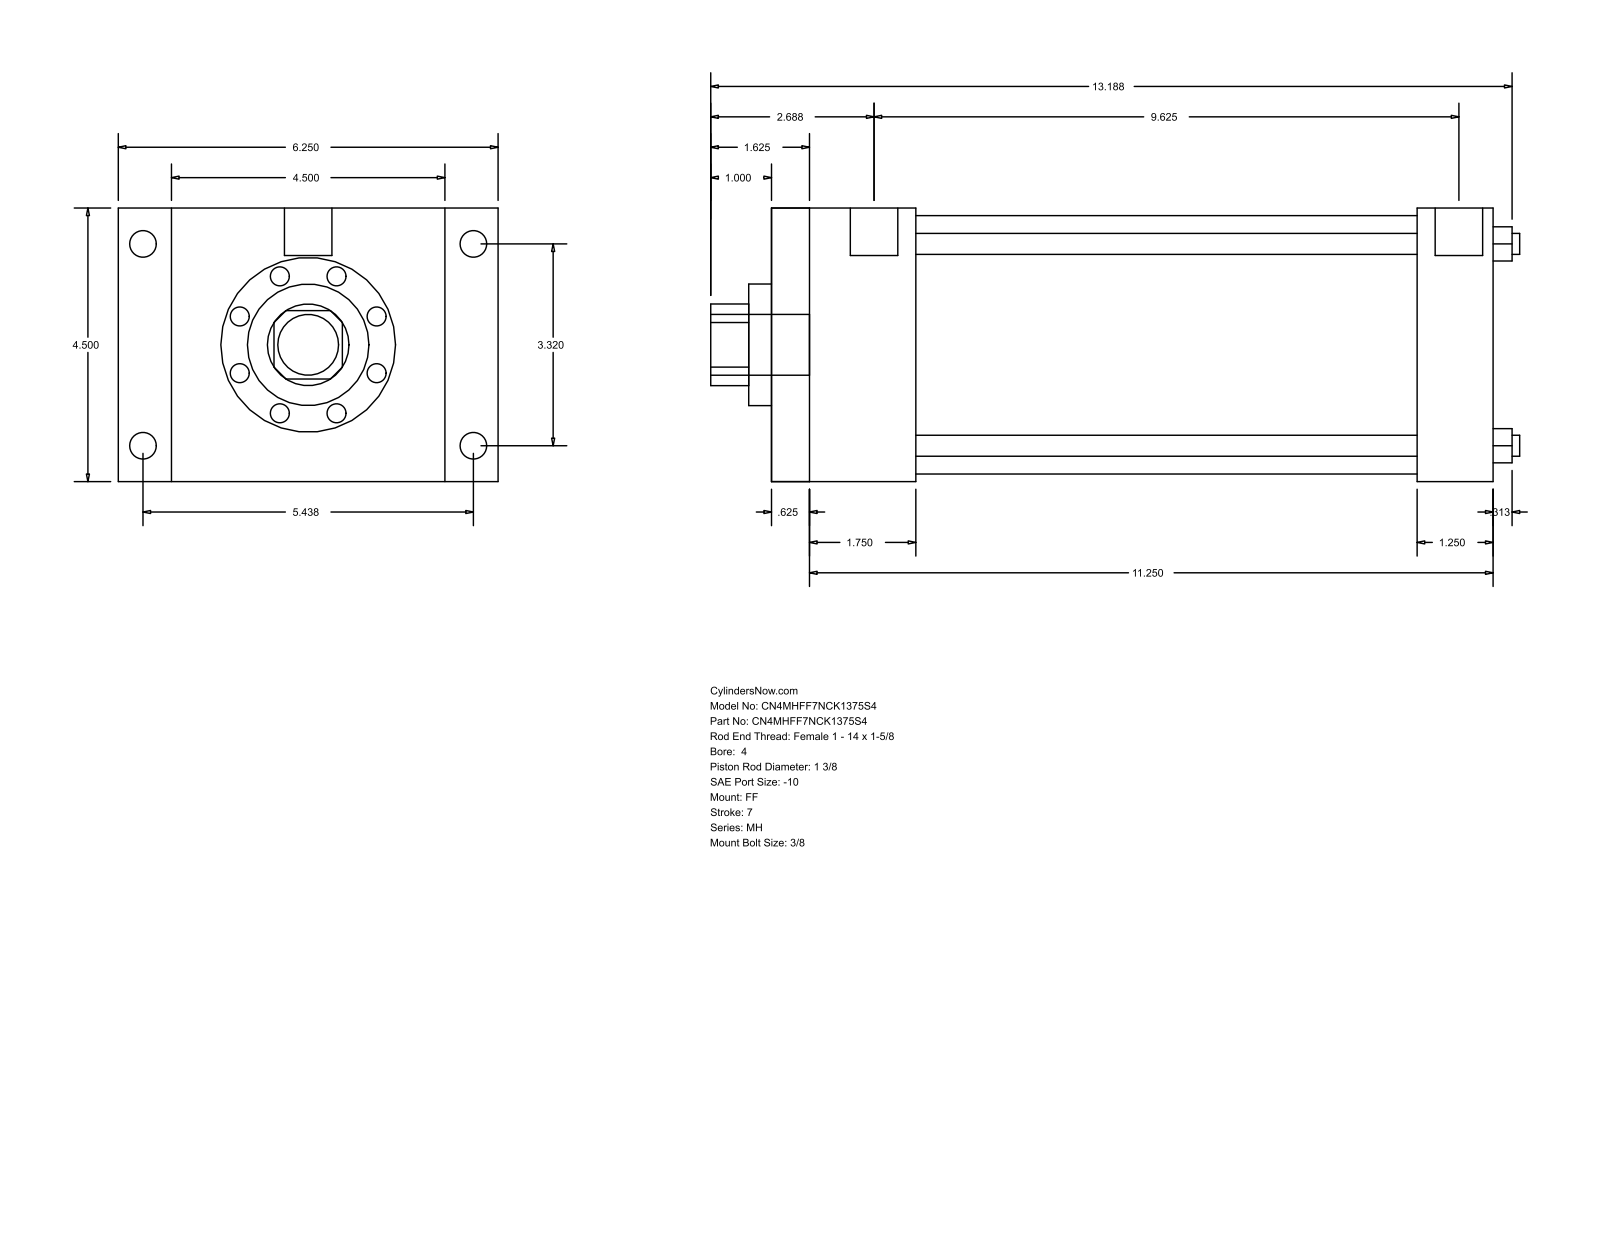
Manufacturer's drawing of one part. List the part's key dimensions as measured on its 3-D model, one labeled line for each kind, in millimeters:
Part name (STEP PRODUCT): MH_FF__0400_1.375
STEP written by: GSSL Pune (CONFIG_CONTROL_DESIGN)
Units: millimetres
Bodies: 0 solids, 92 faces (64 planar, 28 cylindrical, 0 other)
Overall size (bounding box): 338.14 × 158.75 × 114.3
Round holes (diameter × count): ⌀8.76 ×4, ⌀34.92 ×1, ⌀50.8 ×1, ⌀107.95 ×1
Round bosses / shafts (diameter × count): ⌀11.13 ×4, ⌀8.73 ×4, ⌀19.84 ×2, ⌀25.4 ×1
Partial cylindrical surfaces — rounded edges, fillets, slot ends (radius × count): R17.06 ×1
Main face-to-face distances: 114.3, 301.62, 15.87, 285.75, 60.32, 44.45, 241.3, 269.87, 254, 209.55
Hole centre spacings: 59.62, 84.32, 119.25
